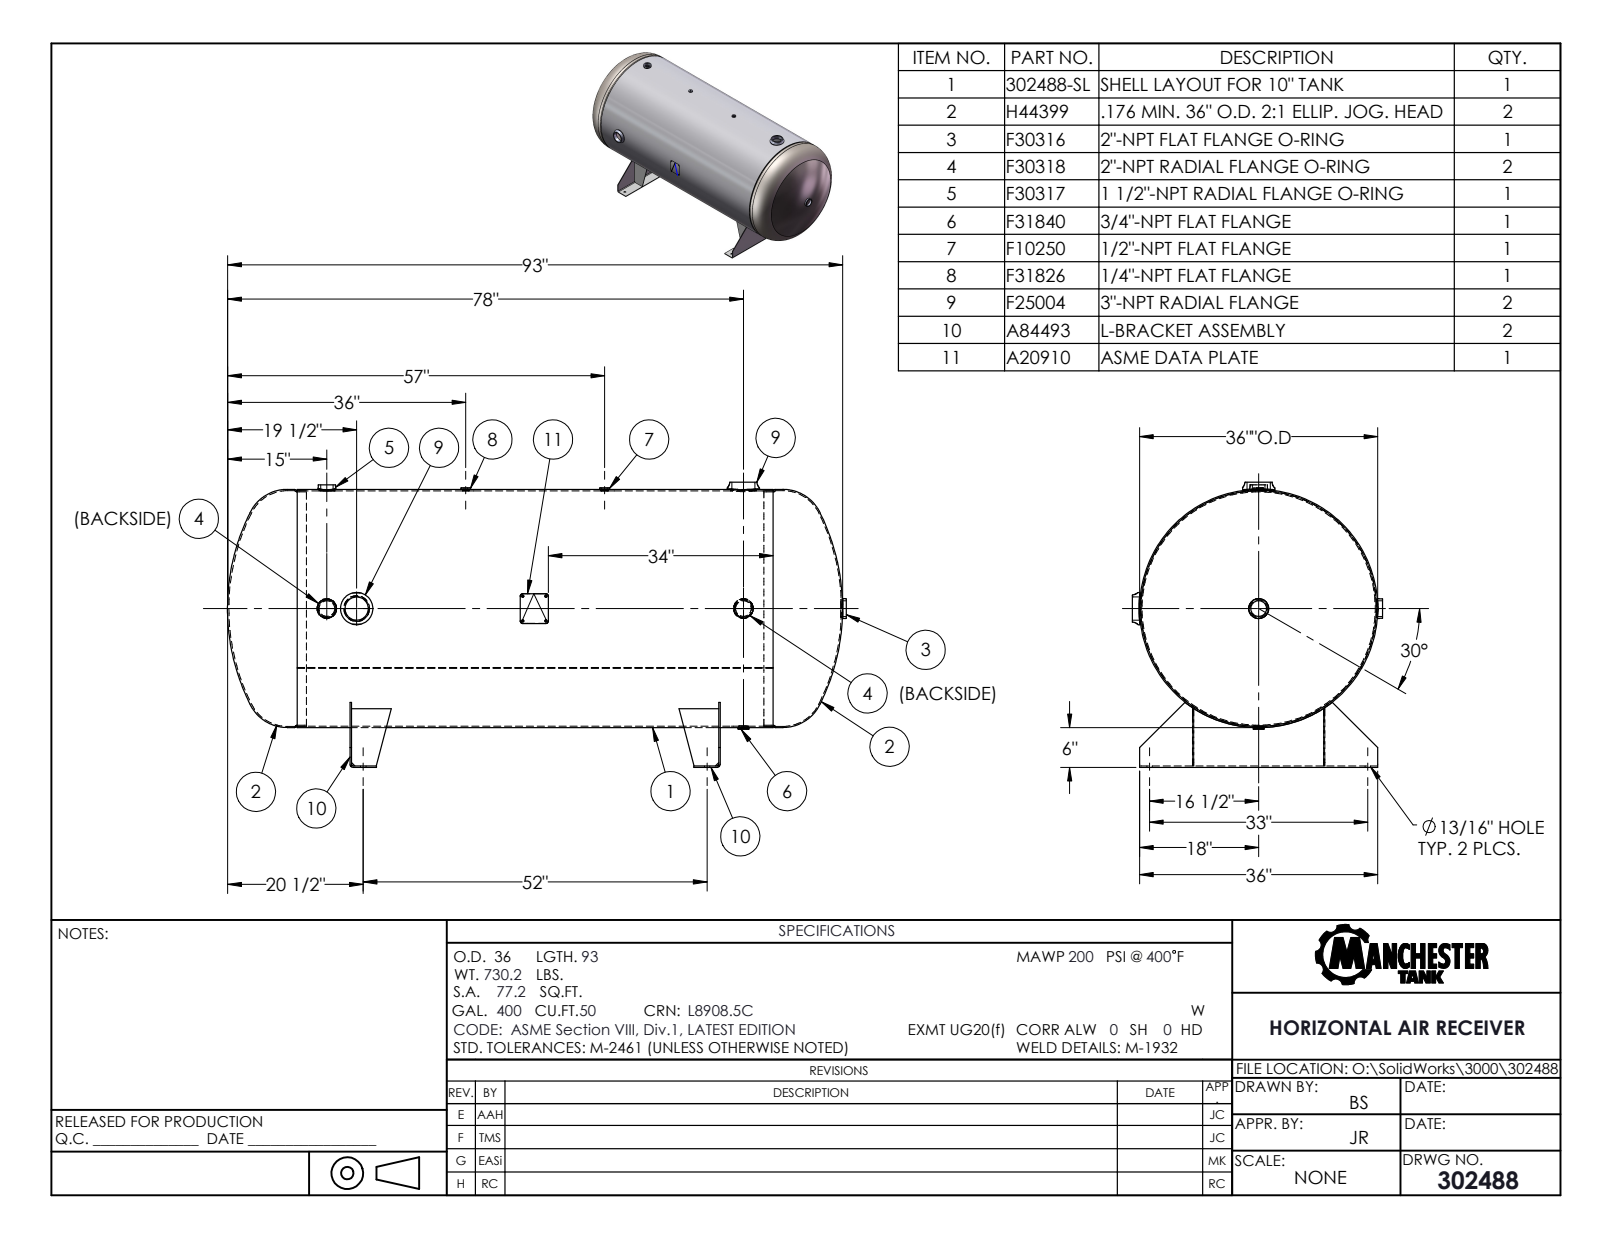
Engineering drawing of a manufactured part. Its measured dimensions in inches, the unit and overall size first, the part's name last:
Units: inches
Overall size (bounding box): 93.625 × 43 × 37.862
Round holes (diameter × count): ⌀0.813 ×4, ⌀2.375 ×3, ⌀3.5 ×2, ⌀0.54 ×1, ⌀0.84 ×1, ⌀1.05 ×1, ⌀1.9 ×1, ⌀35.276 ×1, ⌀35.59 ×1
Round bosses / shafts (diameter × count): ⌀4.25 ×2, ⌀3.625 ×2, ⌀36 ×1, ⌀35.62 ×1, ⌀3.5 ×1, ⌀2.875 ×1, ⌀2.688 ×1, ⌀2.063 ×1
Partial cylindrical surfaces — rounded edges, fillets, slot ends (radius × count): R0.094 ×2, R0.344 ×2, R18.06 ×1
Main face-to-face distances: 0.25, 55.75, 56, 55.5, 20, 0.25, 8, 8.25, 63.75, 64
Hole centre spacings: 17.393, 22.639, 40.056, 59.82, 21, 33, 42, 52
Bodies: 0 solids, 204 faces (53 planar, 69 cylindrical, 82 other)
Part name (STEP PRODUCT): 302488
STEP written by: SolidWorks 2011 (CONFIG_CONTROL_DESIGN)
